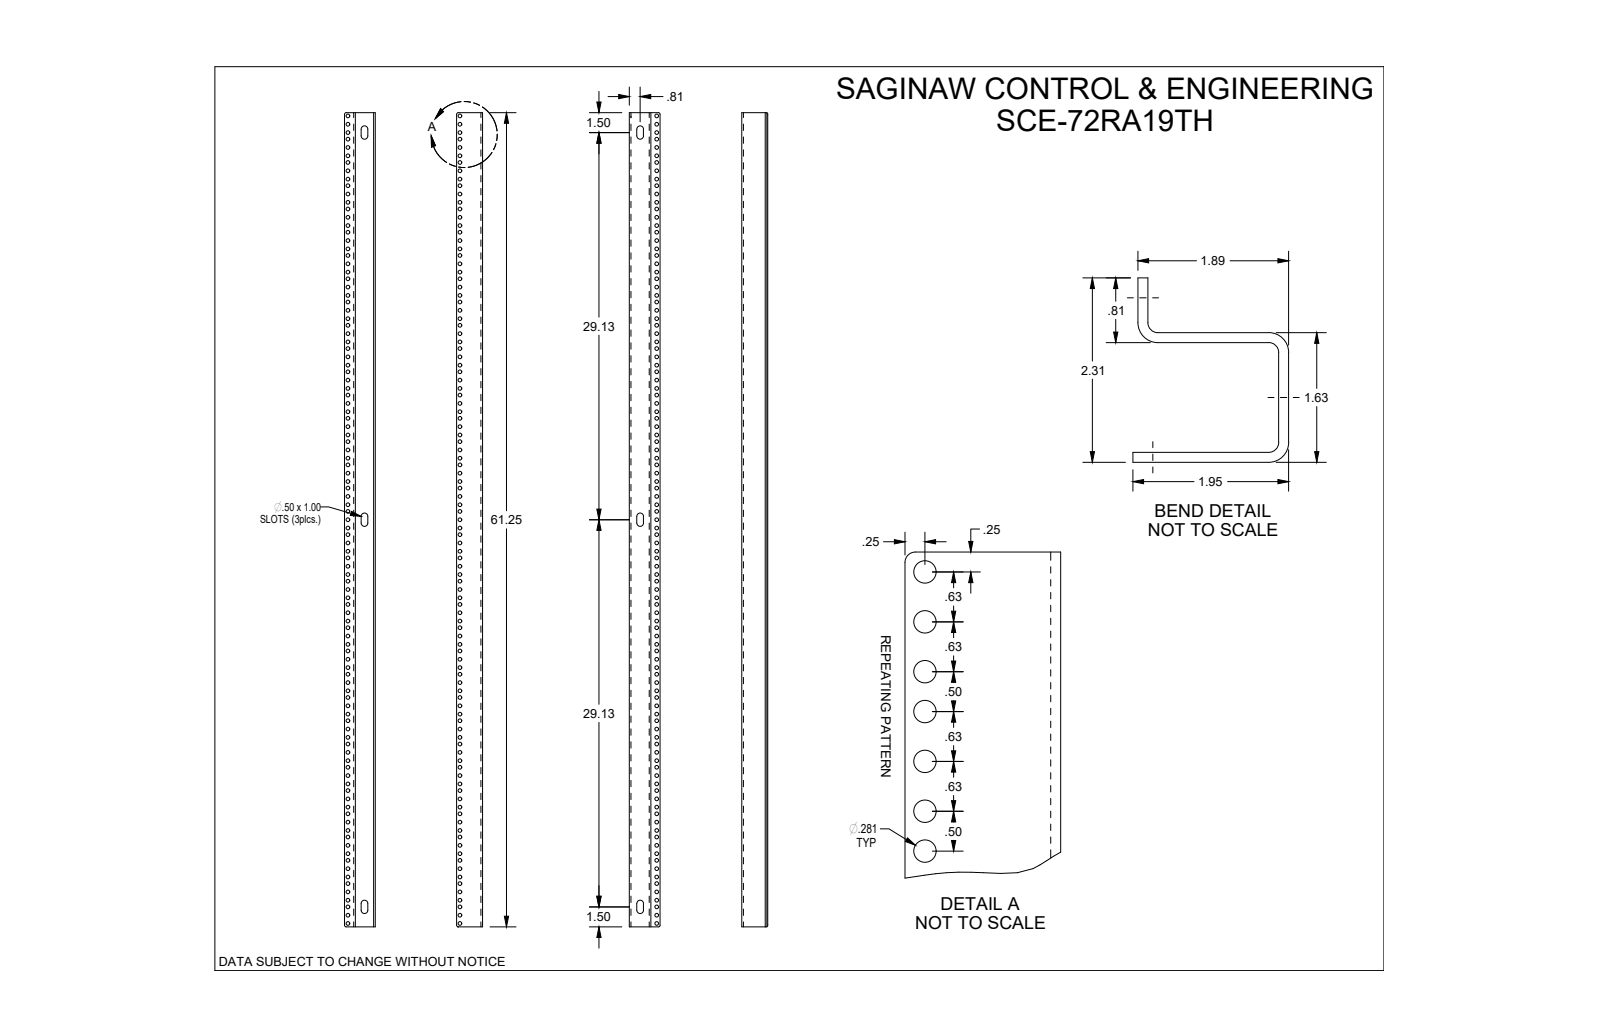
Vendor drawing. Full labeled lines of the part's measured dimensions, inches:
Part name (STEP PRODUCT): SCE-72RA19TH
STEP written by: SolidWorks 2019 (CONFIG_CONTROL_DESIGN)
Units: inches
Bodies: 2 solids, 488 faces (36 planar, 452 cylindrical, 0 other)
Overall size (bounding box): 61.25 × 21.719 × 2.312
Volume: 83.13 in³ · Surface area: 1 412 in²
Round holes (diameter × count): ⌀0.281 ×324
Partial cylindrical surfaces — rounded edges, fillets, slot ends (radius × count): R0.25 ×12, R0.125 ×8, R0.13 ×6
Main face-to-face distances: 0.125, 1.5, 1.625, 1.375, 0.125, 19.828, 1.765, 21.593, 21.719, 21.469
Hole centre spacings: 1.75, 3.5, 5.25, 7, 8.75, 0.625, 0.625, 1.25
